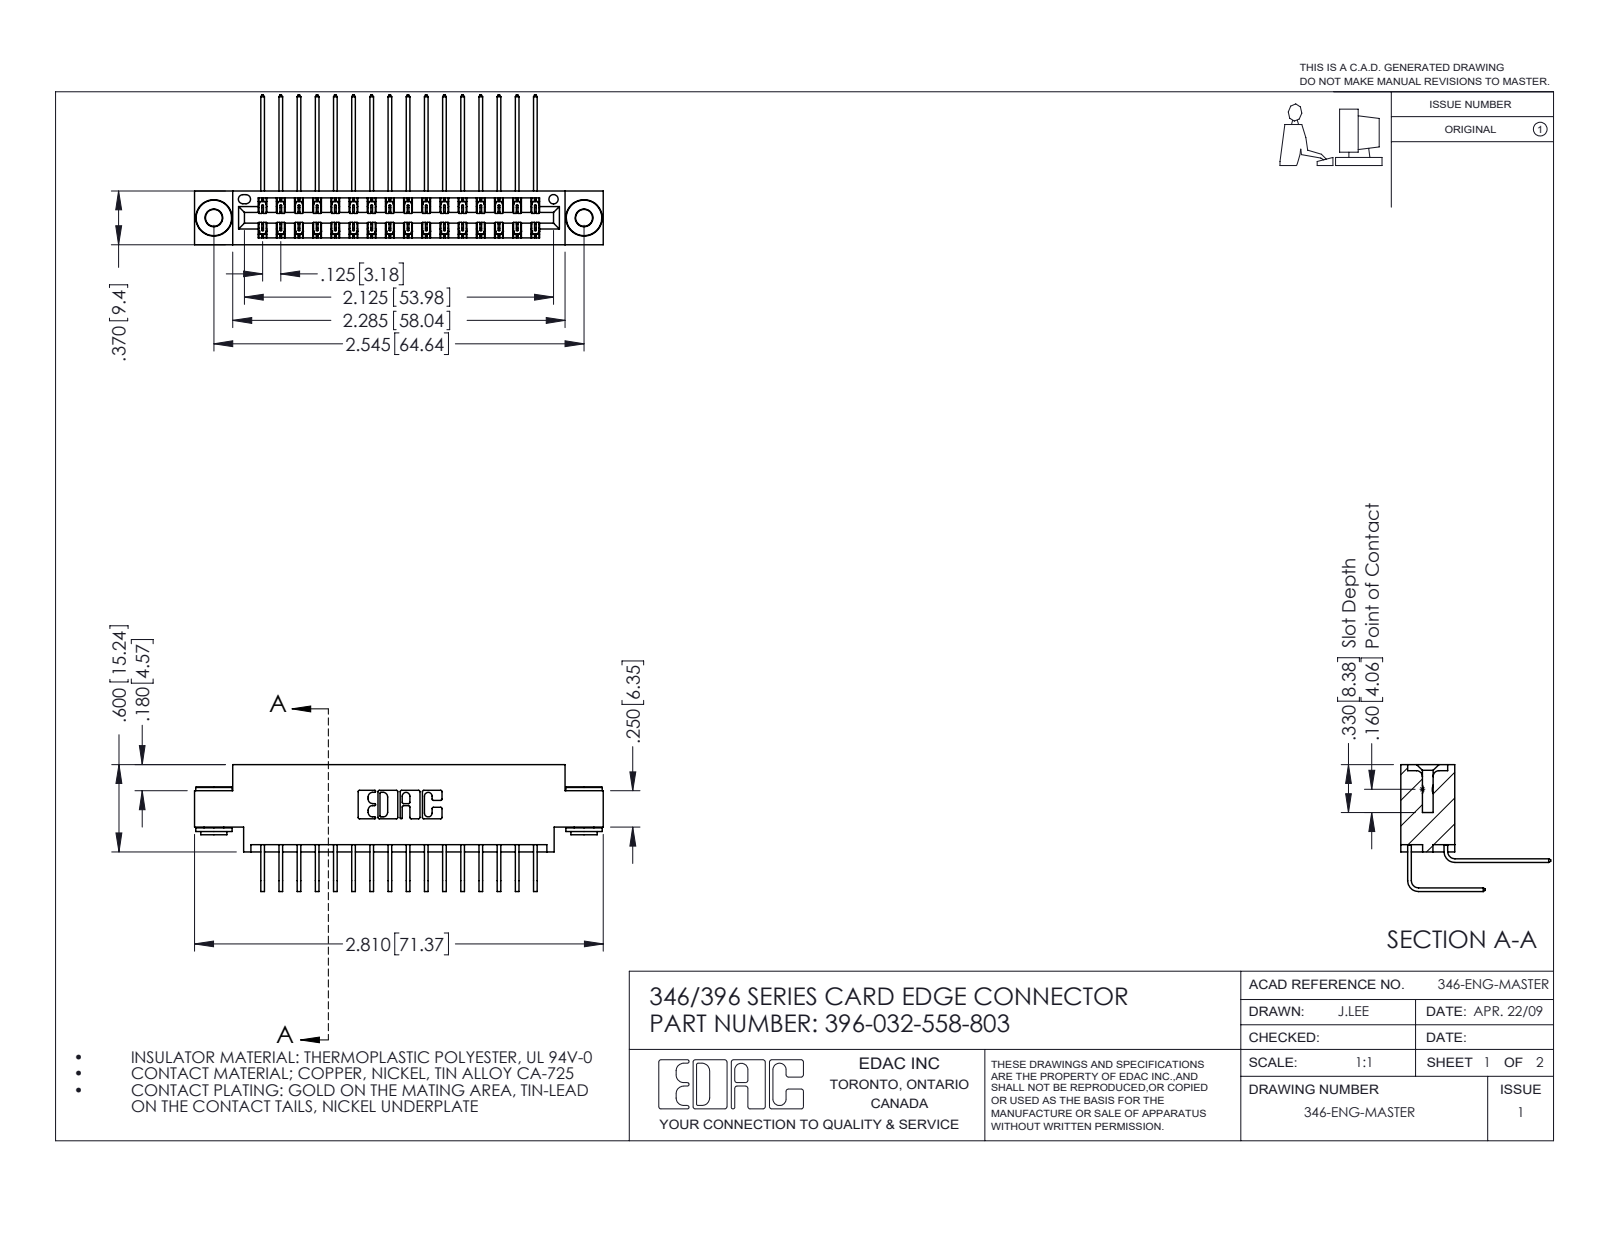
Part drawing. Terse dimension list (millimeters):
name: 345-292-001_558 559 Tail - 1; 346 Part_0.170 Offset - 0.156 Dia-TH; 345-292-001_558 Tail - 2; 396-032-558-803 (+1 more)
written by: SolidWorks 2016 (CONFIG_CONTROL_DESIGN)
unit: mm
bodies: 35 solids, 1892 faces (1274 planar, 610 cylindrical, 8 other)
size: 71.4 × 26.2 × 22.2
volume: 6 800 mm³; area: 10 230 mm²
holes: 2× ⌀2.9, 2× ⌀4, 1× ⌀1.6
bosses: 2× ⌀6.4, 2× ⌀4.6, 2× ⌀3.5
rounds: 48× R0.2, 22× R0.3, 6× R0.2, 6× R0.8, 3× R0.7, 2× R0.4, 2× R0.6, 2× R0.6
face distances: 1.2, 8.2, 9.4, 6.4, 0.6, 1.8, 7.6, 7, 3.8, 5.6
hole spacings: 6.2, 59.4, 64.6
